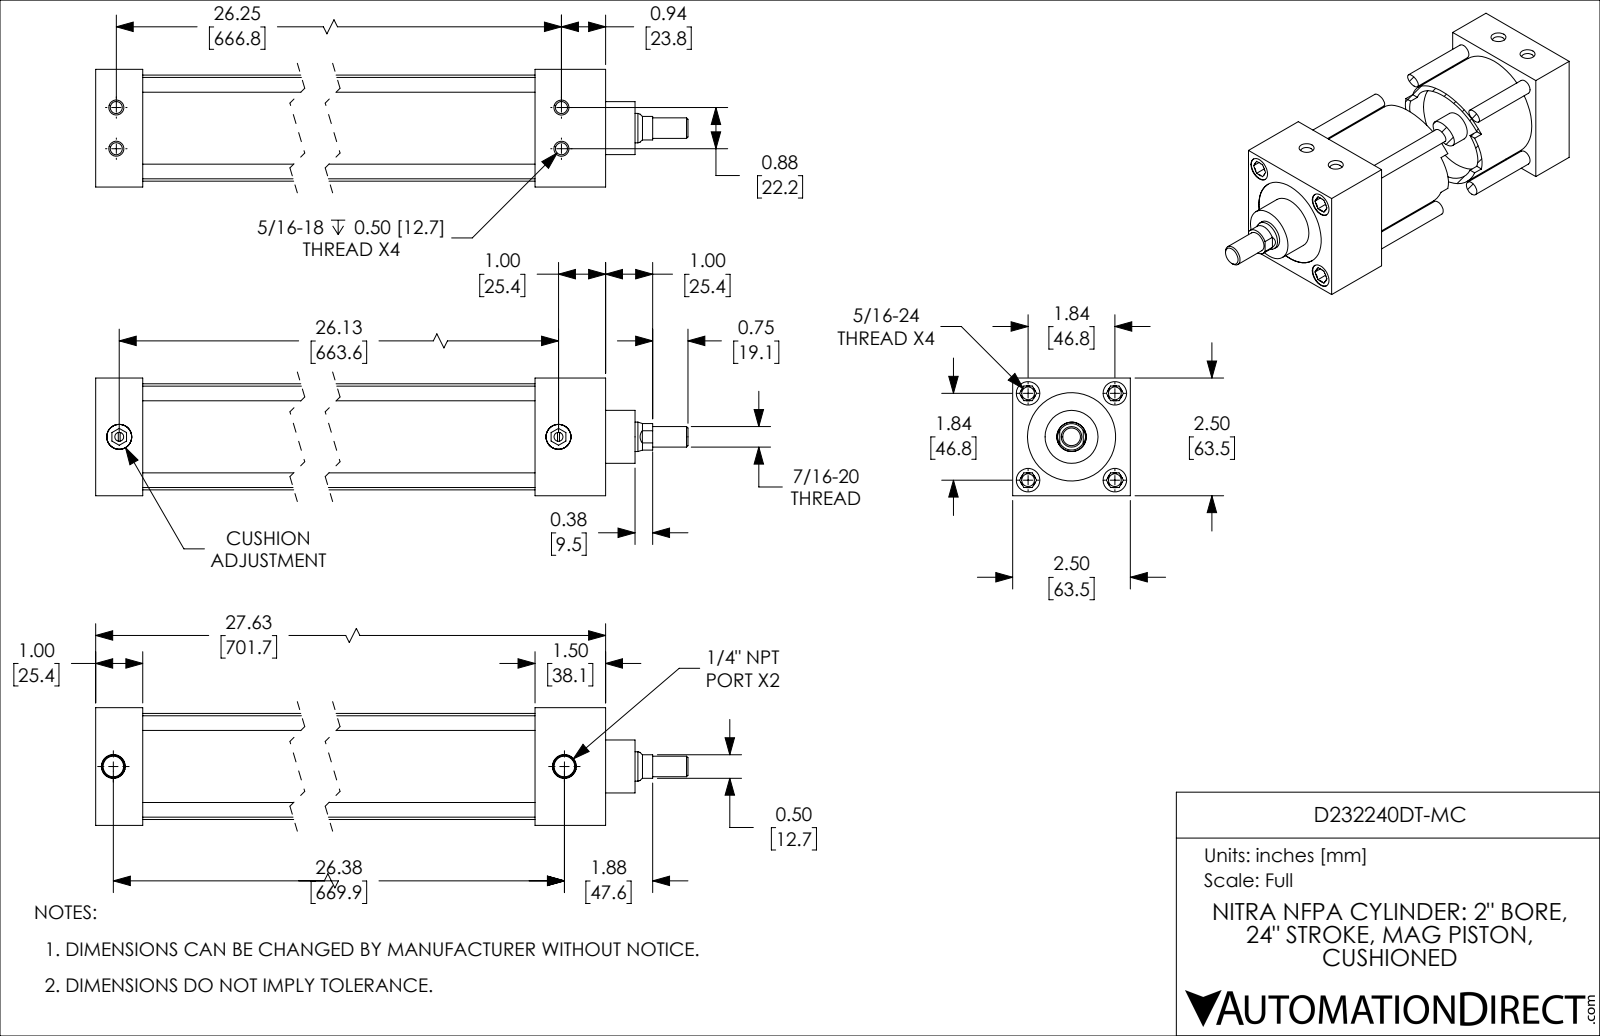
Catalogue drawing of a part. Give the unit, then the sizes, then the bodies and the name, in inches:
Units: inches
Overall size (bounding box): 29.375 × 2.5 × 2.5
Round holes (diameter × count): ⌀0.272 ×7, ⌀0.257 ×4, ⌀0.5 ×4, ⌀0.19 ×2, ⌀0.438 ×2, ⌀0.531 ×2, ⌀0.626 ×1, ⌀1.875 ×1, ⌀2.001 ×1
Round bosses / shafts (diameter × count): ⌀0.312 ×4, ⌀0.532 ×2, ⌀2.251 ×1, ⌀1.999 ×1, ⌀1.125 ×1, ⌀0.624 ×1, ⌀0.437 ×1
Partial cylindrical surfaces — rounded edges, fillets, slot ends (radius × count): R0.281 ×1
Main face-to-face distances: 2.5, 1, 26.125, 25.125, 1.125, 2.125, 24, 1.5, 27.625, 26.625
Hole centre spacings: 1.84, 1.844, 1.301, 0.441, 0.443, 0.875, 1.304, 2.602
Volume: 55.14 in³ · Surface area: 565.7 in²
Bodies: 4 solids, 248 faces (90 planar, 78 cylindrical, 80 other)
Part name (STEP PRODUCT): D232240DT-MC_BODY; D232240DT-MC_PISTON_KK1; D232240DT-MC; D232240DT-MC_CUSHION
STEP written by: SolidWorks 2019 (CONFIG_CONTROL_DESIGN)
